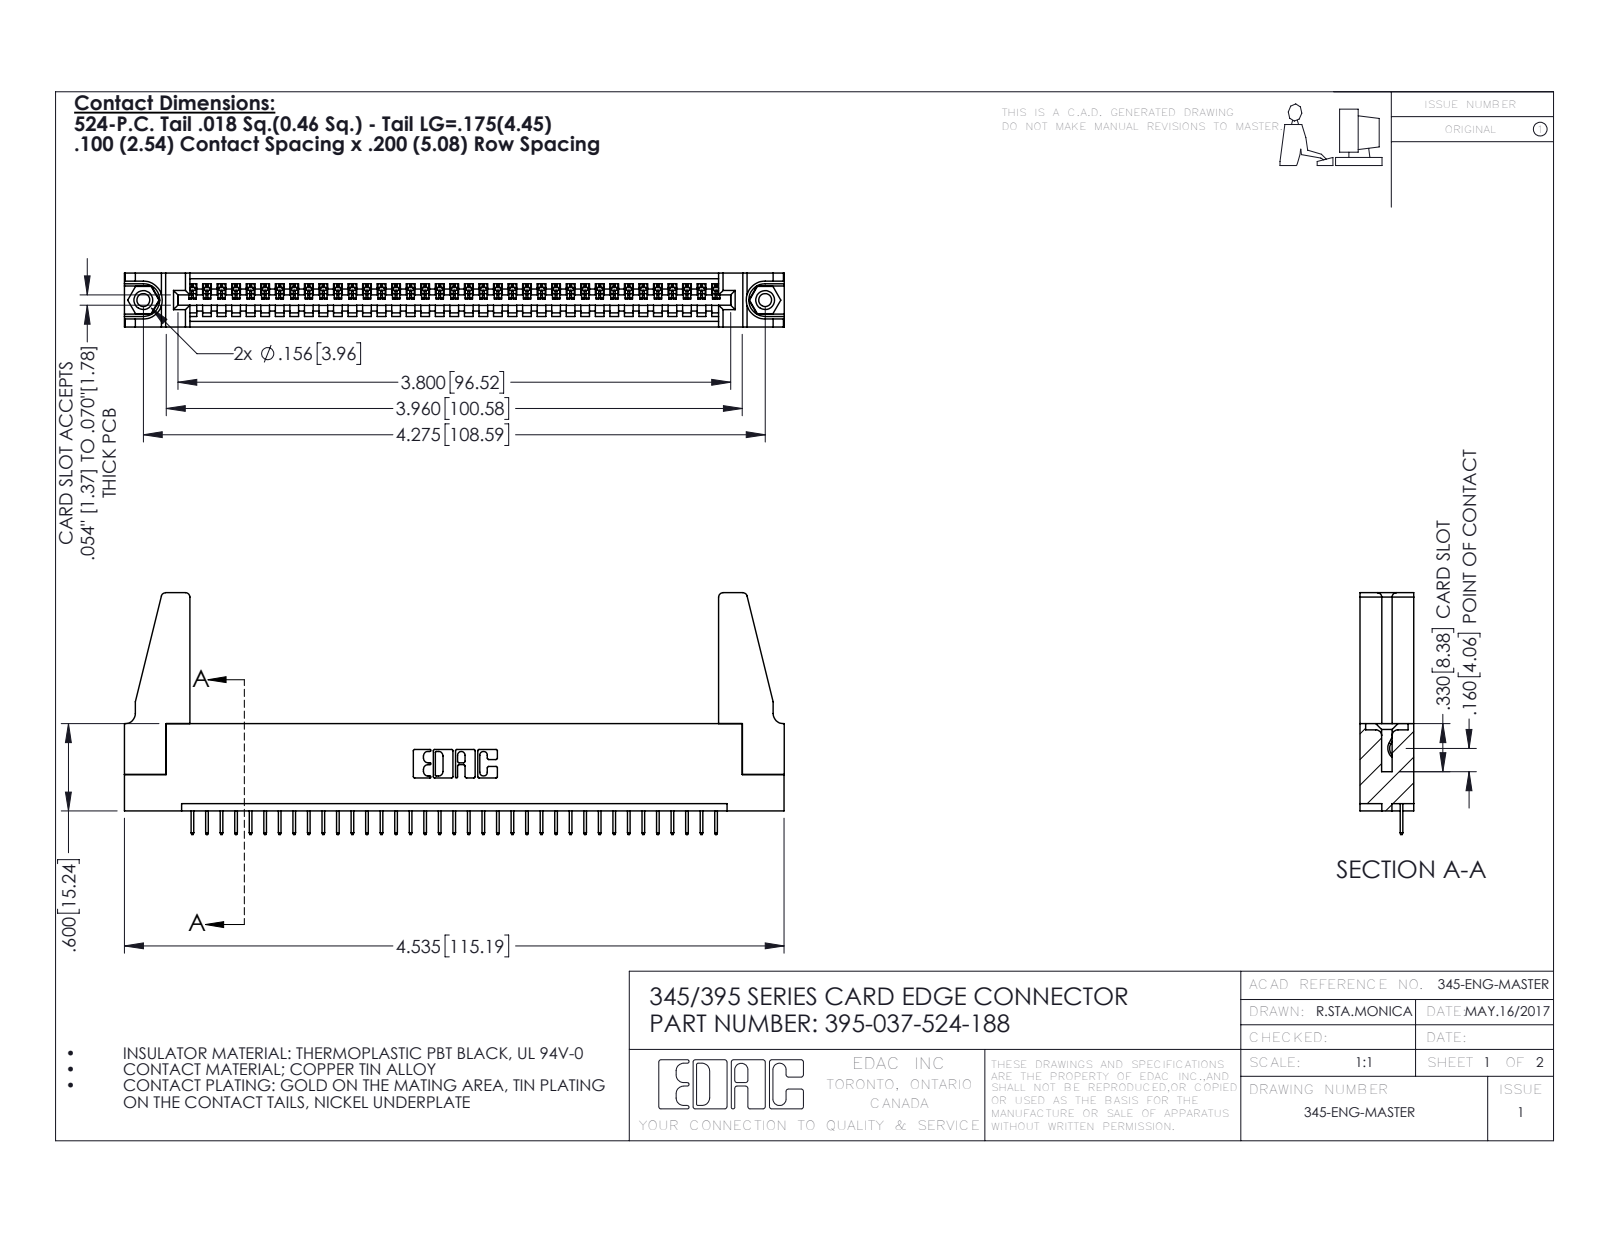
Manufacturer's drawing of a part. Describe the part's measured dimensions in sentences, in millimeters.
The part is named "345 Part_Flush Mounting Lugs - 0.156 Dia-TH; 395-037-524-188; 345-250-001_345-250-001-102; 345-292-001_345-293-124 (+1 more)". Its 3-D file was written by "SolidWorks 2016 (CONFIG_CONTROL_DESIGN)". It is 42 solids with 2544 faces: 1854 planar, 674 cylindrical and 16 other. Overall it measures 115.2 by 42.2 by 9.4 millimeters. Its volume is 14 000 cubic millimeters and its surface area 16 890 square millimeters. Round holes: 2 of diameter 2.3, 2 of diameter 3.2, 2 of diameter 4, 1 of diameter 1.6. Round bosses or shafts: 2 of diameter 3.9. Partial cylindrical surfaces (rounded edges, fillets, slot ends): 74 of radius 0.2, 22 of radius 0.3, 8 of radius 0.8, 6 of radius 0.2, 6 of radius 0.8, 3 of radius 0.7, 2 of radius 0.8, 2 of radius 1. The main face-to-face distances are 1.8, 9.4, 7.6, 5.1, 2.5, 6.9, 0.6, 5.7, 1.8, 3.8. The hole center spacings are 6.9, 102.6, 108.6.
